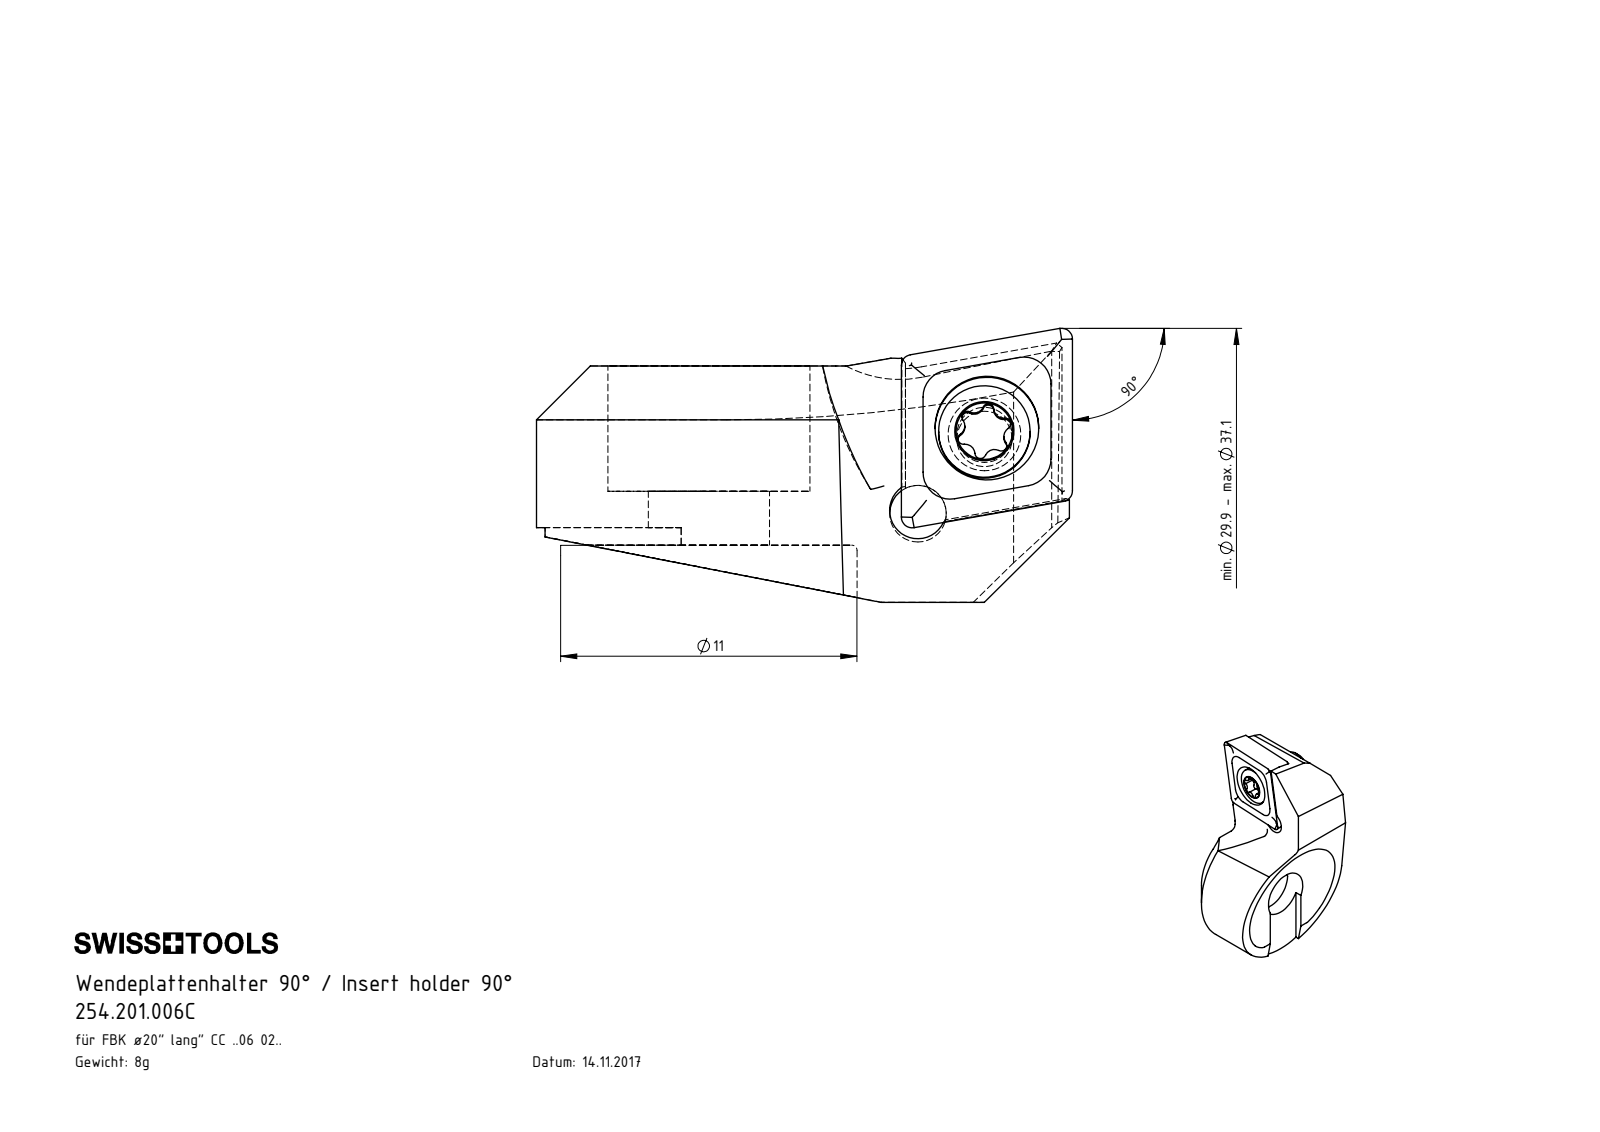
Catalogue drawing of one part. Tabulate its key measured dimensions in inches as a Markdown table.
| quantity | value |
| --- | --- |
| part name | F20-WCA.001.008_C_fertigbearbeitet; CCMT060204; WCA-ER2.001.006_A; 254.201.006C |
| STEP written by | SolidWorks 2017 (CONFIG_CONTROL_DESIGN) |
| units | inches |
| bodies | 5 solids, 146 faces (49 planar, 46 cylindrical, 51 other) |
| overall size | 0.783 × 0.504 × 0.4 |
| volume | 0.064 in³ |
| surface area | 2.04 in² |
| round holes (diameter × count) | 0.081 × 1, 0.083 × 1, 0.11 × 1, 0.152 × 1, 0.177 × 1, 0.295 × 1 |
| round bosses / shafts (diameter × count) | 0.134 × 1, 0.098 × 1 |
| partial cylindrical surfaces (radius × count) | 0.008 × 6, 0.014 × 5, 0.02 × 2, 0.014 × 1, 0.041 × 1, 0.197 × 1, 0.217 × 1, 0.252 × 1 |
| main face-to-face distances | 0.09, 0.262, 0.039, 0.222, 0.183, 0.144, 0.079, 0.345, 0.306, 0.162 |
| hole center spacings | 0.151, 0.157 |
